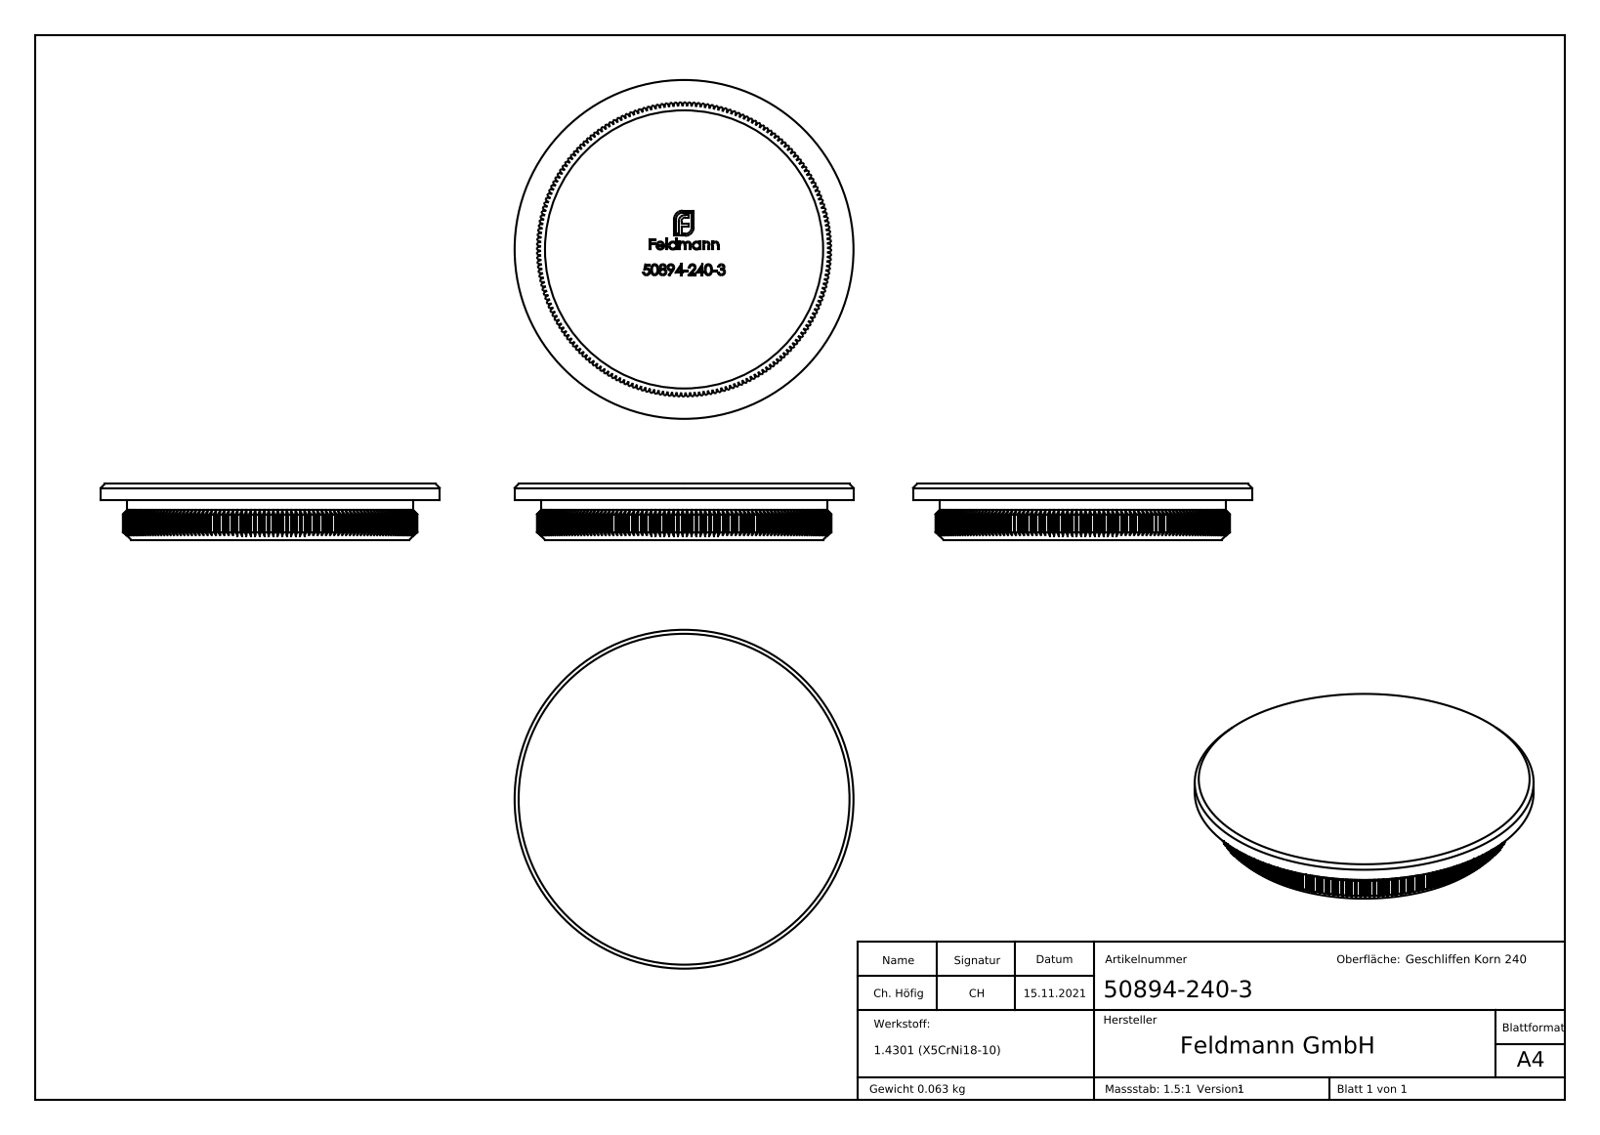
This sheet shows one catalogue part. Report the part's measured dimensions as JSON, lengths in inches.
{"part_name": "50894-240-3", "step_written_by": "SolidWorks 2018 (CONFIG_CONTROL_DESIGN)", "units": "inches", "bodies": {"solids": 1, "faces": 1105, "planar": 561, "cylindrical": 202, "other": 342}, "overall_size": [1.669, 1.669, 0.276], "volume_in3": 0.485, "surface_area_in2": 6.281, "round_bosses_or_shafts": [[1.669, 1], [1.409, 1]], "partial_cylinders_radius": [[0.724, 1]], "face_to_face_distances": [0.276, 0.079, 0.197, 0.365, 0.365, 0.193, 0.272, 0.364, 0.074, 0.126]}
